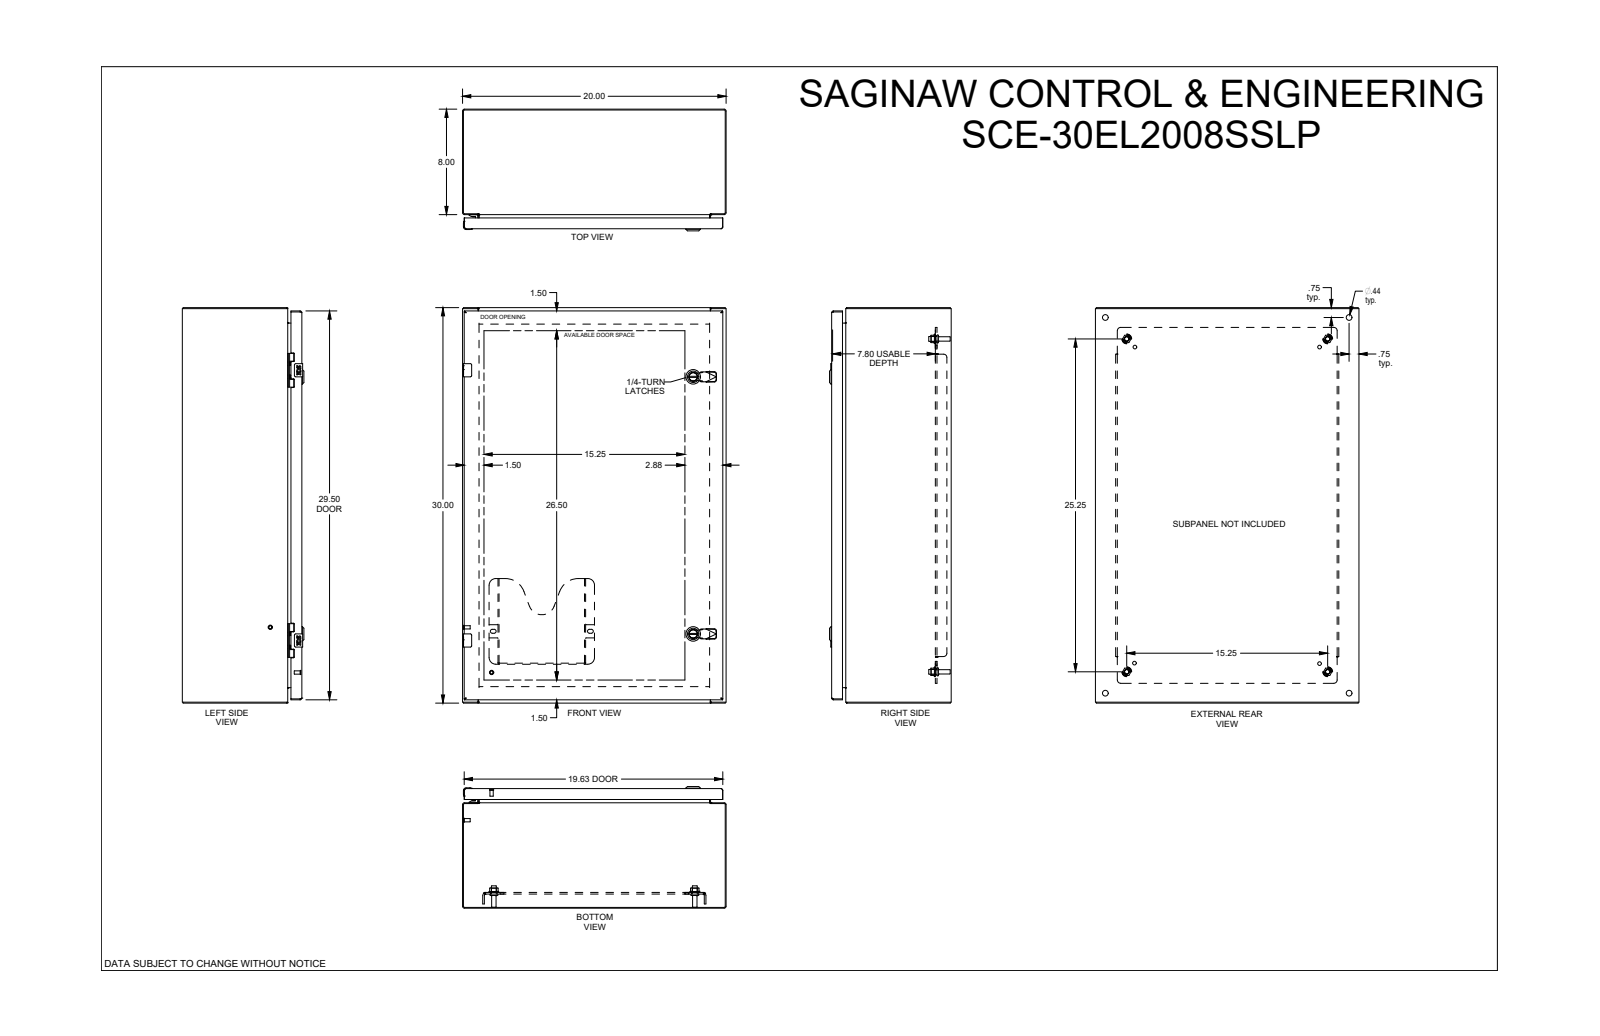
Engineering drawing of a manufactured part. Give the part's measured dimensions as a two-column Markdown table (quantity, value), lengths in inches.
| quantity | value |
| --- | --- |
| part name | SCE-30EL2008SSLP |
| STEP written by | SolidWorks 2019 (CONFIG_CONTROL_DESIGN) |
| units | inches |
| bodies | 0 solids, 2806 faces (1297 planar, 749 cylindrical, 760 other) |
| overall size | 30 × 20 × 9.23 |
| round holes (diameter × count) | 0.172 × 4, 0.205 × 4, 0.244 × 4, 0.266 × 4, 0.281 × 4, 0.367 × 4, 0.437 × 4, 0.5 × 4, 0.375 × 3, 0.156 × 2, 0.197 × 2, 0.218 × 2 |
| round bosses / shafts (diameter × count) | 0.17 × 6, 0.366 × 4, 0.332 × 4, 0.25 × 4, 0.248 × 4, 0.196 × 3, 1.102 × 2, 0.866 × 2 |
| partial cylindrical surfaces (radius × count) | 0.012 × 56, 0.015 × 32, 0.01 × 28, 0.04 × 23, 0.02 × 20, 0.029 × 12, 0.07 × 10, 0.145 × 10 |
| main face-to-face distances | 0.075, 0.075, 8.923, 8.998, 9.073, 8.998, 0.125, 1, 19.925, 7.923 |
| hole center spacings | 20.5, 0.985, 0.02, 0.875, 4.493, 16.953, 3.173, 14.644 |
